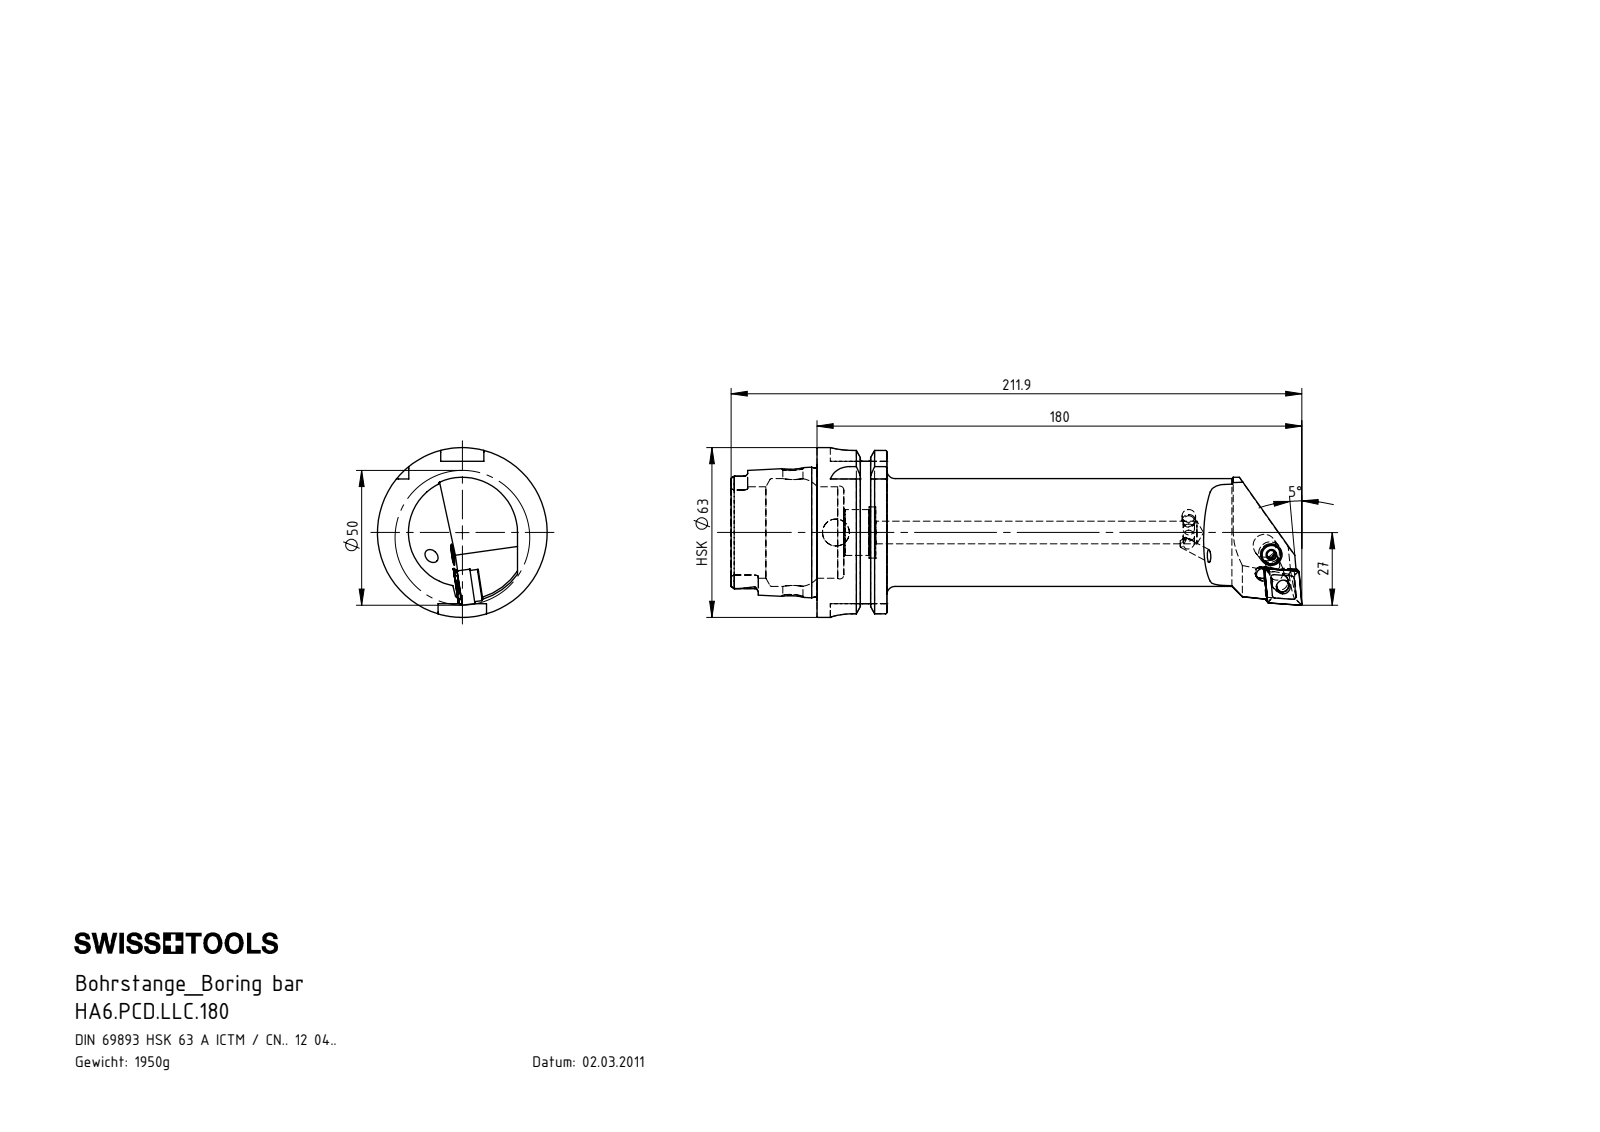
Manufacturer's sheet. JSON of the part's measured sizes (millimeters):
{"part_name": "WCD-ER1.101.000; WCD-ER2.101.003_A; HA6.PCD.LLC.180; KVT_MB_600_050 (+4 more)", "step_written_by": "SolidWorks 2017 (AUTOMOTIVE_DESIGN)", "units": "millimeters", "bodies": {"solids": 8, "faces": 380, "planar": 116, "cylindrical": 108, "other": 156}, "overall_size": [211.9, 63, 63], "volume_mm3": 248747, "surface_area_mm2": 46877, "round_holes": [[4.2, 2], [8.4, 2], [4, 1], [5, 1], [5.16, 1], [6.4, 1], [7, 1], [7.5, 1], [10, 1], [17, 1], [19, 1], [34, 1]], "round_bosses_or_shafts": [[63, 1], [54.95, 1], [47.94, 1], [8, 1], [7.9, 1], [6.4, 1], [5, 1], [4.5, 1]], "partial_cylinders_radius": [[1.4, 6], [0.4, 4], [1, 4], [8, 4], [2.5, 2], [2.82, 2], [2.88, 2], [20.5, 2]], "face_to_face_distances": [25.95, 16, 9.95, 31.9, 41.85, 57.85, 52.8, 21.8, 11.85, 4.49], "hole_center_spacings": [12.81, 12.87]}
